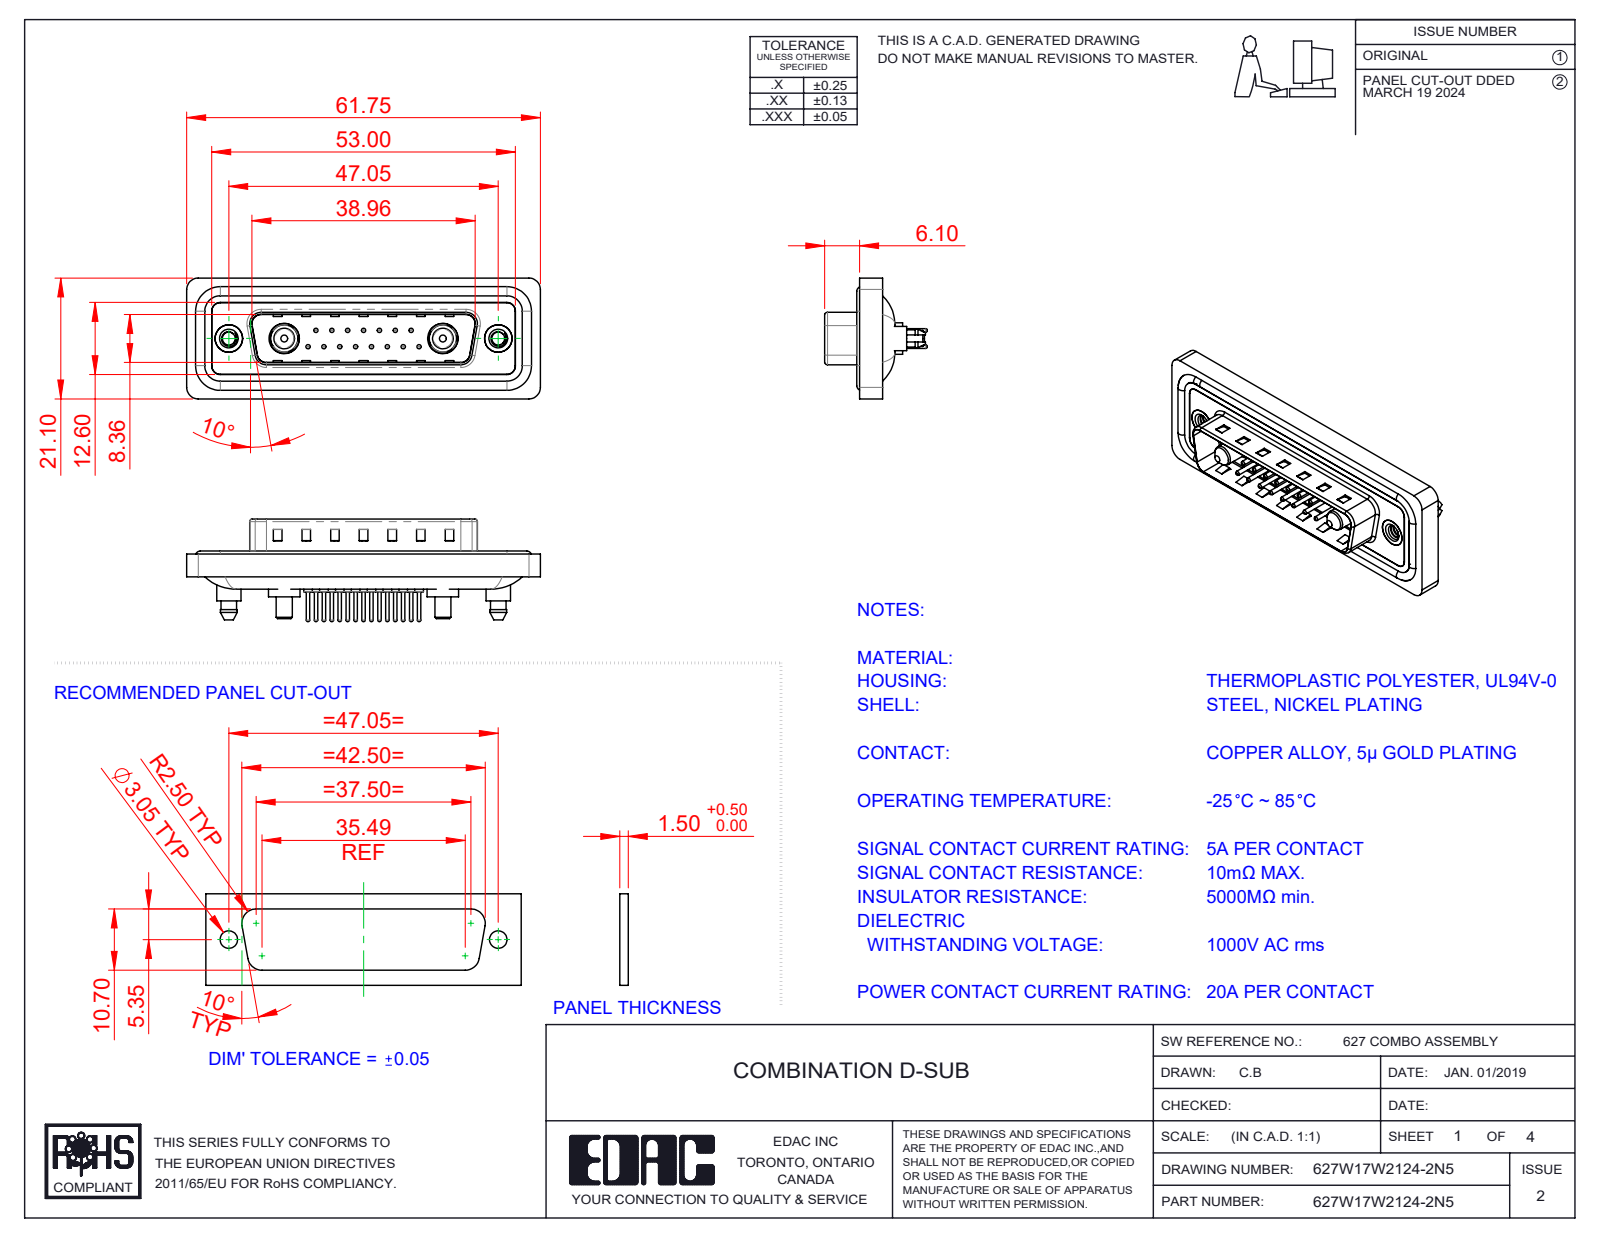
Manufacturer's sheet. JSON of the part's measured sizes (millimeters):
{"part_name": "627Combo Waterproof Housing_25 Contacts; 627Combo Contact Row 1_24; 627Combo Contact Row 2_24; 627Combo Housing_17W2 (+5 more)", "step_written_by": "SolidWorks 2023 (CONFIG_CONTROL_DESIGN)", "units": "millimeters", "bodies": {"solids": 26, "faces": 1166, "planar": 350, "cylindrical": 468, "other": 348}, "overall_size": [61.75, 21.1, 17.9], "volume_mm3": 7400, "surface_area_mm2": 12247, "round_holes": [[0.75, 15], [1.6, 15], [2, 15], [2.26, 2], [4, 2], [4.8, 2], [4.85, 2], [5, 2], [5.3, 2]], "round_bosses_or_shafts": [[1.5, 15], [0.6, 15], [1.6, 4], [5.5, 2], [5.4, 2], [5.2, 2], [4.9, 2], [4.75, 2]], "partial_cylinders_radius": [[1.5, 24], [2, 18], [1.6, 10], [0.5, 8], [0.25, 4], [0.6, 4], [0.65, 4], [0.9, 4]], "face_to_face_distances": [0.4, 1.5, 1.1, 1.6, 0.5, 3.1, 2.9, 0.82, 9.58, 4.1], "hole_center_spacings": [3.16, 2.77, 5.54, 8.31, 5.04, 7.49, 11.08, 5.03]}
